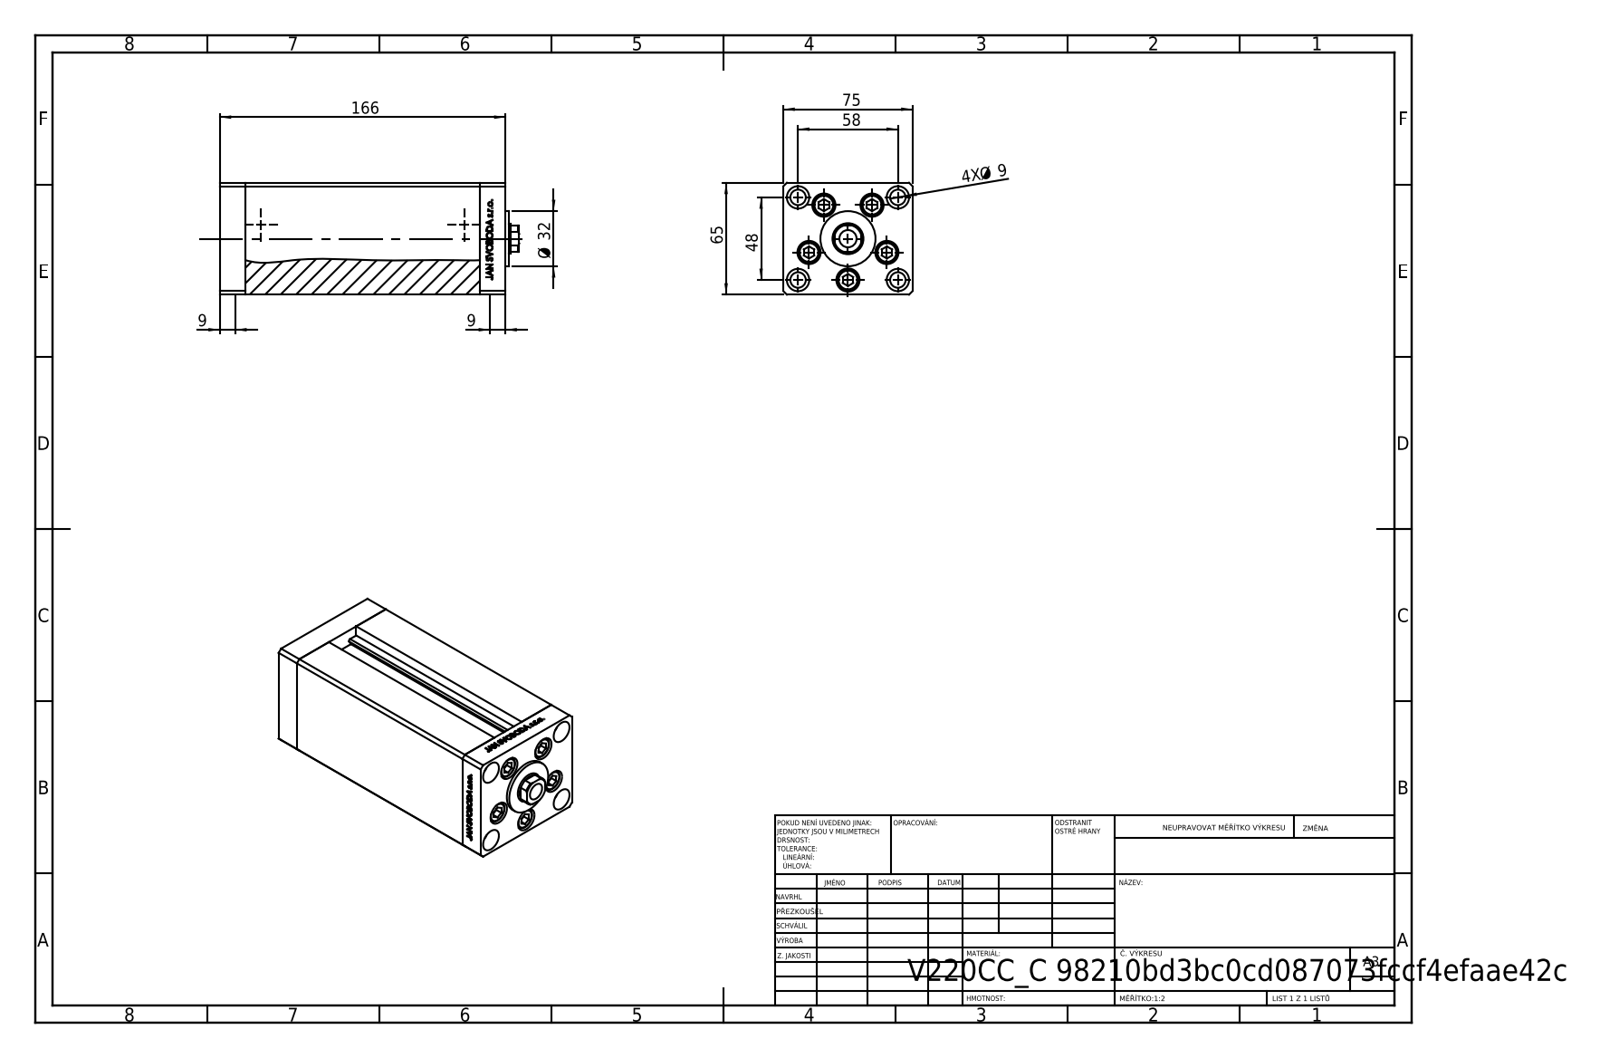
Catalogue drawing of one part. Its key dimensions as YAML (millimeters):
part_name: "V220C_C CAST PRO VYSUNUTI; V220C BACK; V220C FRONT; ALLEN BOLT (+1 more)"
step_written_by: "SolidWorks 2019 (CONFIG_CONTROL_DESIGN)"
units: millimeters
bodies: {solids: 14, faces: 1173, planar: 546, cylindrical: 159, other: 468}
overall_size: [174, 75, 65]
volume: 682197
surface_area: 140869
round_holes:
  - {diameter: 9, count: 9}
  - {diameter: 13.5, count: 5}
  - {diameter: 13, count: 4}
  - {diameter: 10, count: 1}
  - {diameter: 18, count: 1}
round_bosses_or_shafts:
  - {diameter: 12.5, count: 5}
  - {diameter: 8, count: 5}
  - {diameter: 32, count: 1}
partial_cylinders:
  - {radius: 0.93, count: 2}
  - {radius: 8.5, count: 1}
face_to_face_distances: [75, 65, 136, 15, 151, 166, 9, 142, 6, 10.5]
hole_center_spacings: [24, 37.64, 15.67, 17.22, 27.71, 28.83, 29, 32.63]
